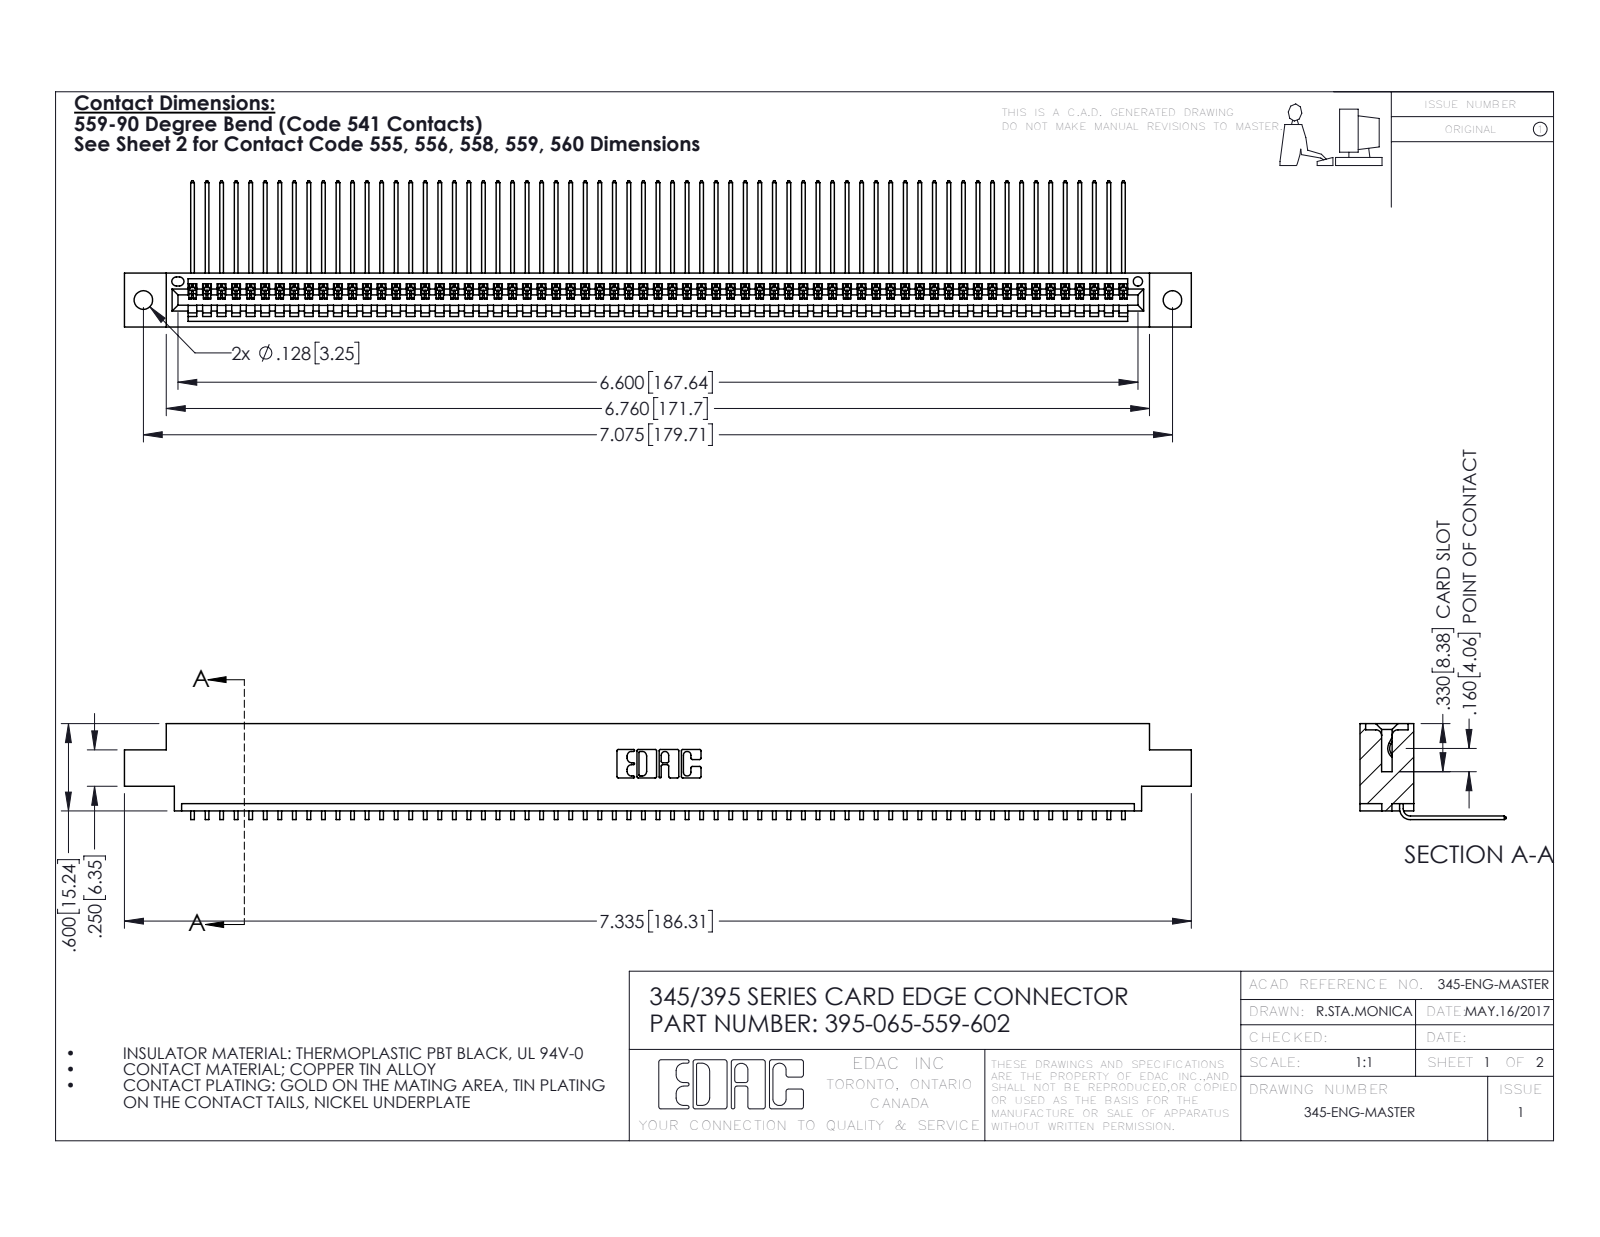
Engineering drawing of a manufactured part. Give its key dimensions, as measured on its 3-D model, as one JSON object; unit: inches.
{"part_name": "345-292-001_558 559 Tail - 1; 395-065-559-602; 345 Part_0.170 Offset - 0.128 Dia", "step_written_by": "SolidWorks 2016 (CONFIG_CONTROL_DESIGN)", "units": "inches", "bodies": {"solids": 66, "faces": 4030, "planar": 2814, "cylindrical": 1216, "other": 0}, "overall_size": [7.335, 1.005, 0.659], "volume_in3": 1.095, "surface_area_in2": 39.21, "round_holes": [[0.128, 2], [0.064, 1]], "partial_cylinders_radius": [[0.006, 130], [0.01, 22], [0.007, 6], [0.031, 6], [0.026, 3], [0.031, 2], [0.04, 2], [0.014, 1]], "face_to_face_distances": [0.072, 0.298, 0.37, 0.2, 0.098, 0.272, 0.025, 0.225, 0.175, 0.149], "hole_center_spacings": [0.27, 6.839, 7.075]}
